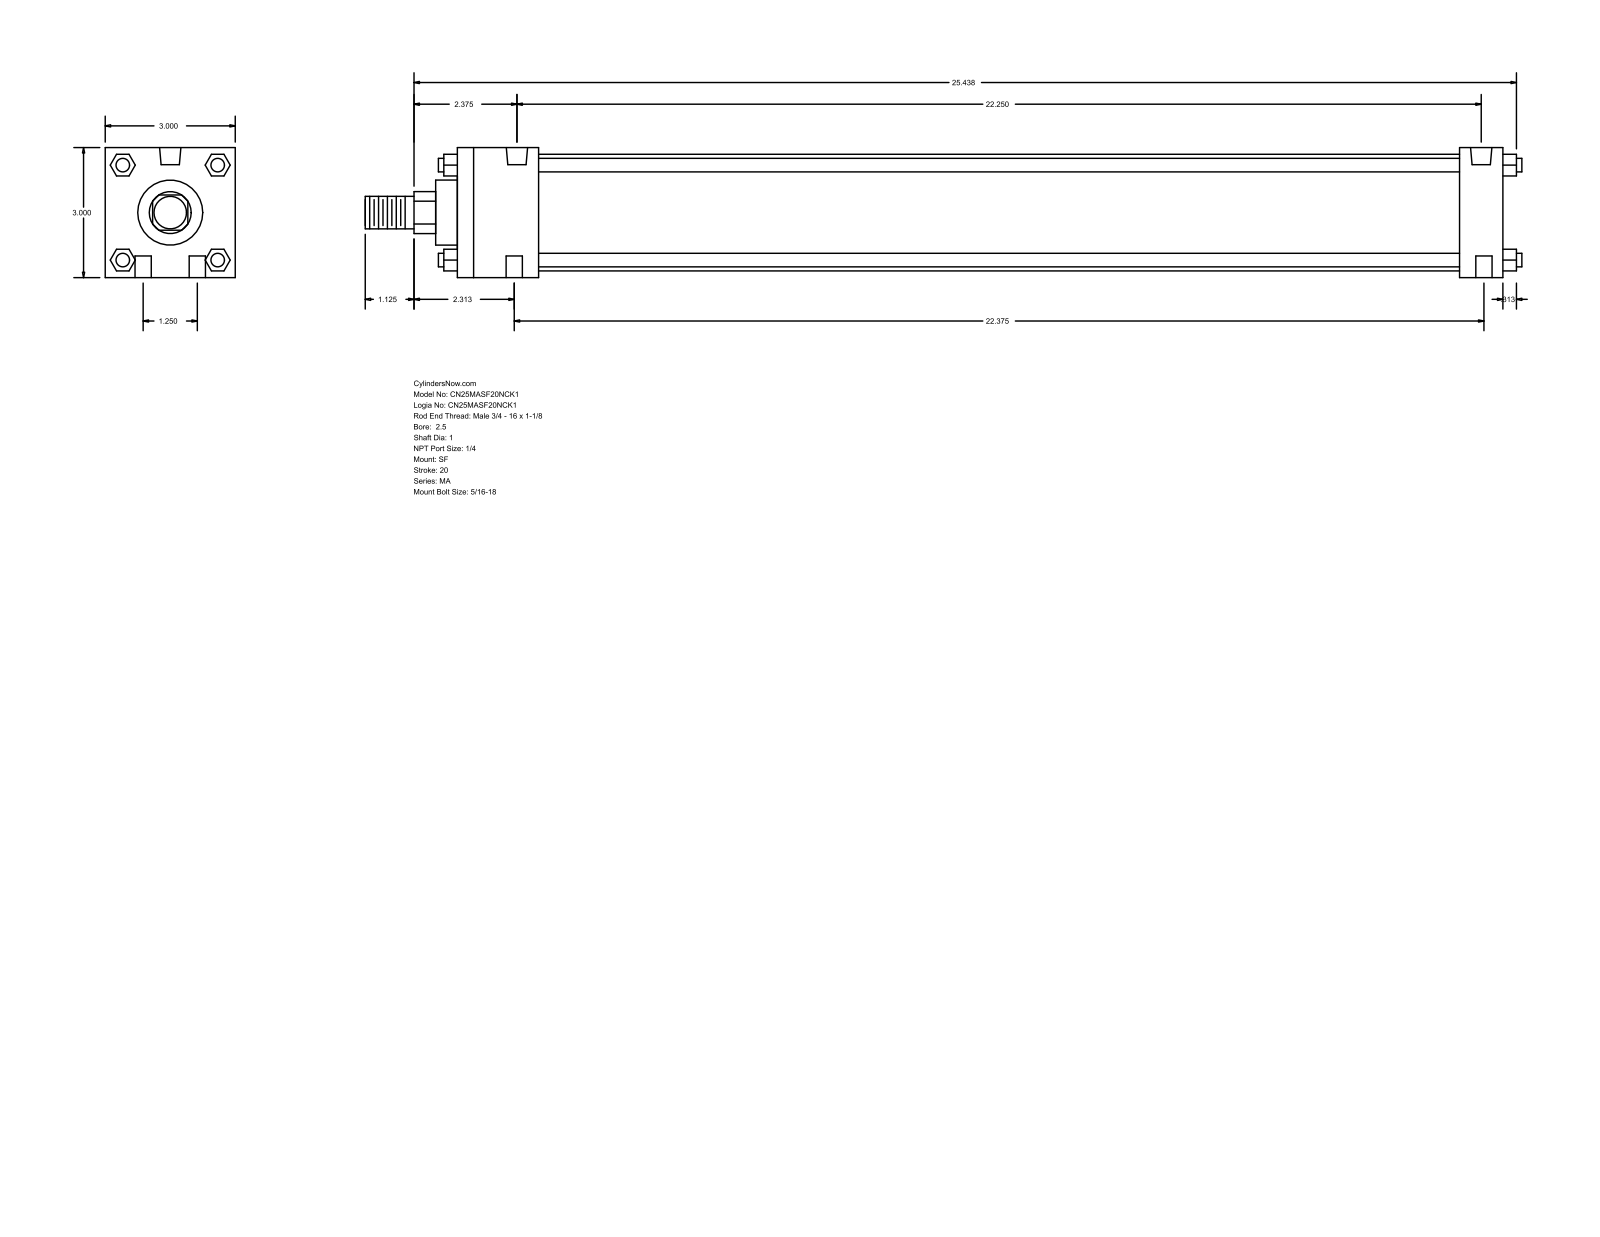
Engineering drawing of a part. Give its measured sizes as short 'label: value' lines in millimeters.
name: MA_SF__0250_1
written by: GSSL Pune (CONFIG_CONTROL_DESIGN)
unit: mm
bodies: 0 solids, 124 faces (94 planar, 30 cylindrical, 0 other)
size: 677.86 × 76.2 × 76.2
holes: 4× ⌀9.53, 2× ⌀7.94, 2× ⌀12.49
bosses: 4× ⌀7.94, 1× ⌀68.33, 1× ⌀38.1, 1× ⌀25.4, 1× ⌀19.05
rounds: 1× R12.29
face distances: 76.2, 612.77, 12.7, 25.4, 587.37, 47.63, 539.74, 565.14, 27.81, 48.17
hole spacings: 15.96, 31.76, 565.15, 566.95, 566.96, 568.32, 569.21
